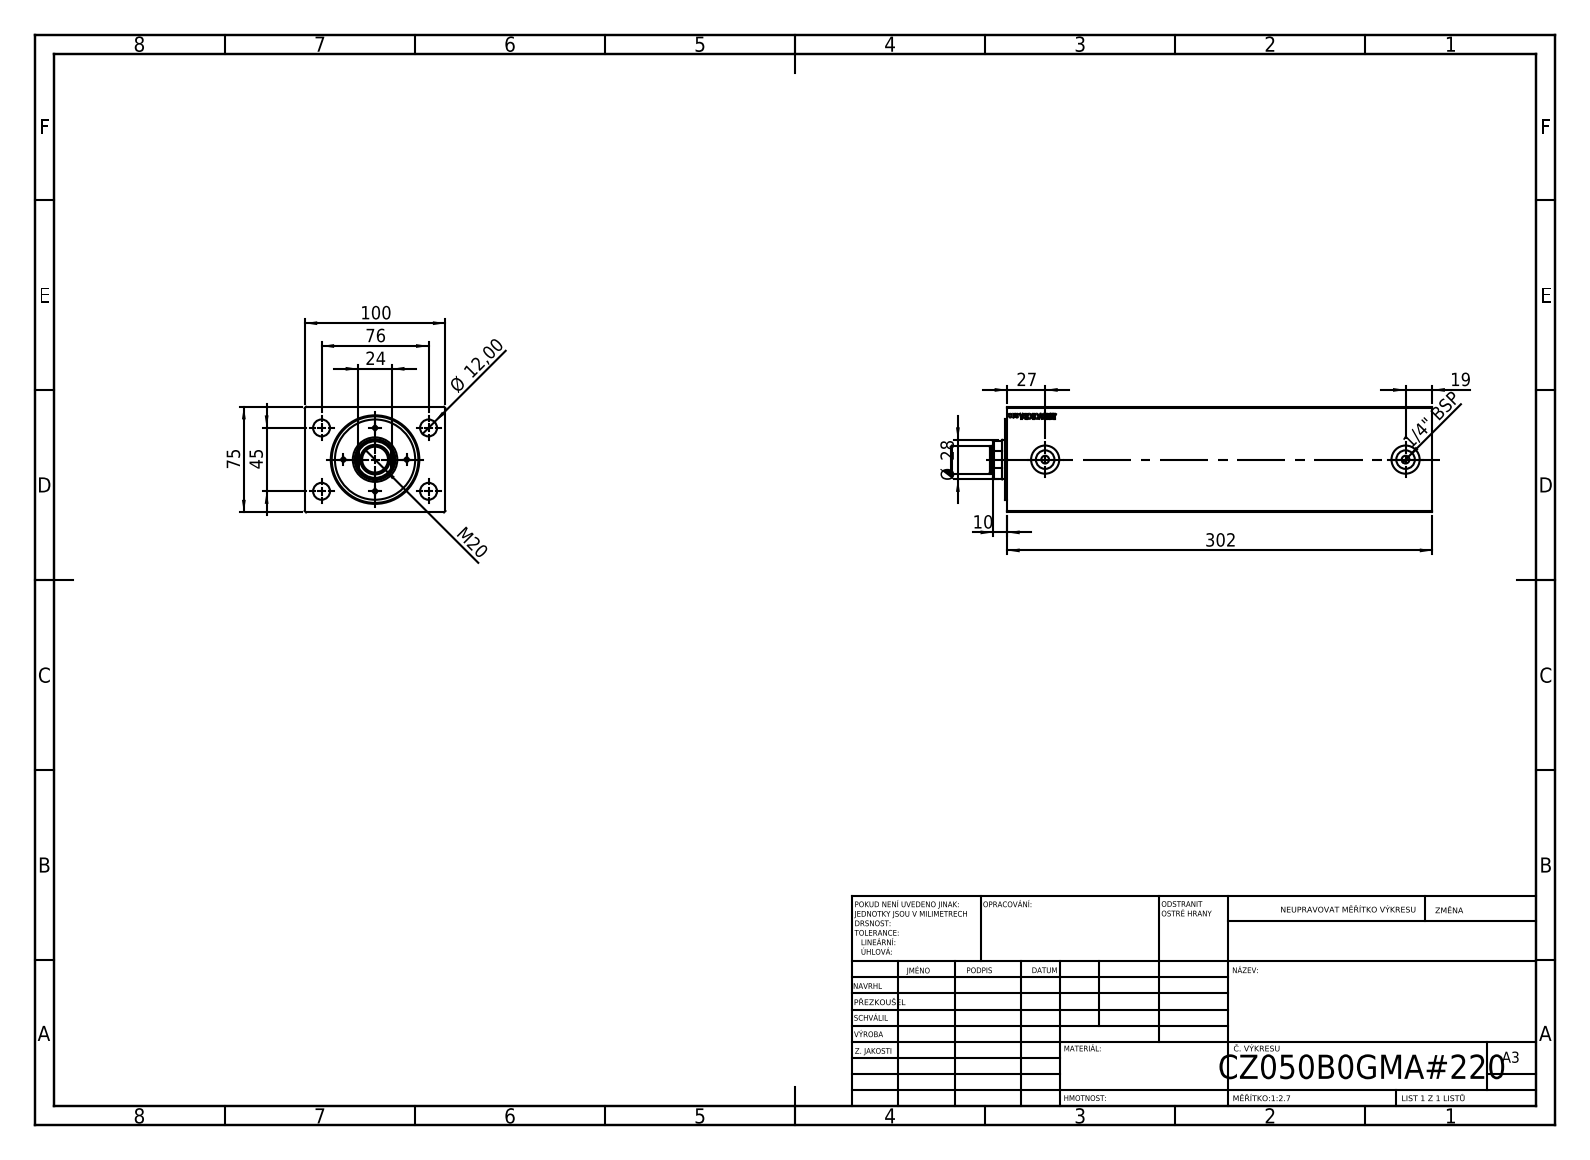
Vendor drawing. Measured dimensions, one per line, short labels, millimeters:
name: V500CZ_B_VC; V500CZ_MALE_METRIC; V500CZ
written by: SolidWorks 2019 (CONFIG_CONTROL_DESIGN)
unit: mm
bodies: 4 solids, 888 faces (404 planar, 62 cylindrical, 422 other)
size: 342 × 100 × 75
volume: 1 946 000 mm³; area: 219 185 mm²
holes: 4× ⌀3, 4× ⌀12, 2× ⌀5.5, 2× ⌀13.16, 2× ⌀20, 1× ⌀18.5, 1× ⌀28, 1× ⌀29, 1× ⌀36, 1× ⌀50, 1× ⌀61.5
bosses: 1× ⌀57, 1× ⌀20, 1× ⌀18
rounds: 1× R13.5
face distances: 75, 100, 302, 284.2, 17.8, 10, 8.2, 1.8, 276, 293.8
hole spacings: 22.5, 27.32, 31.82, 38, 44.16, 45, 58.9, 64.55
